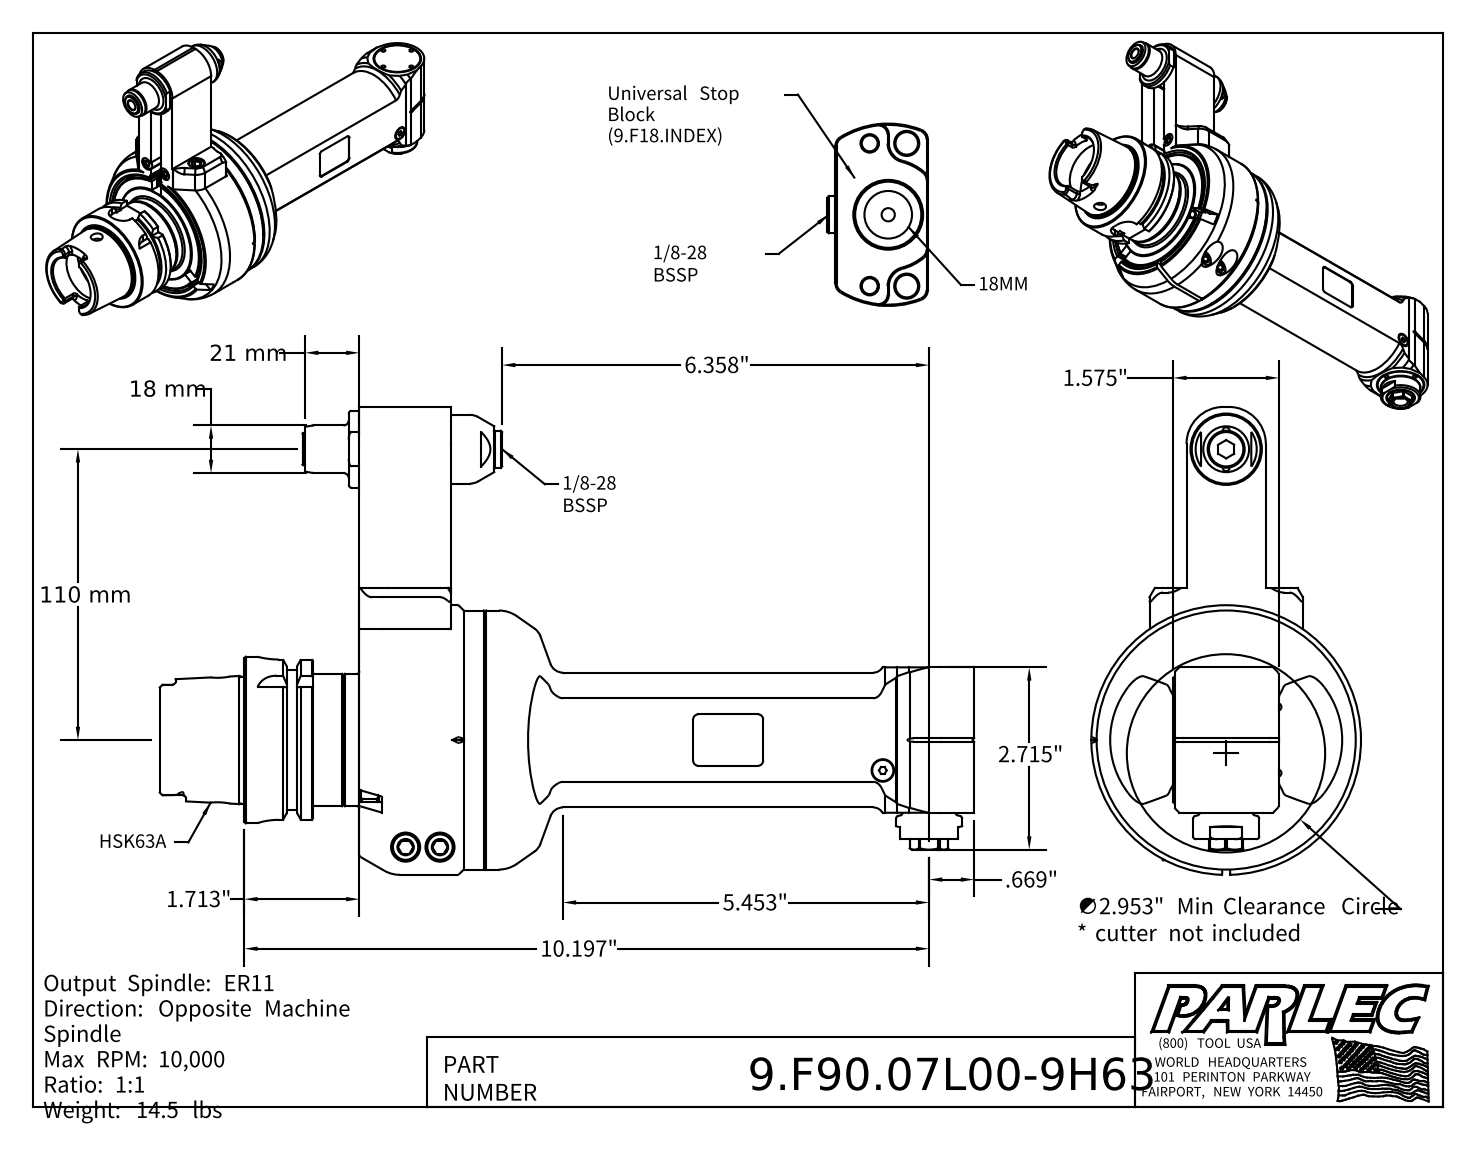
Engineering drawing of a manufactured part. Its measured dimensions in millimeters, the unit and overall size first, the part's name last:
Units: millimetres
Overall size (bounding box): 308 × 176.98 × 102
Round holes (diameter × count): ⌀2.6 ×6, ⌀4.2 ×4, ⌀6.5 ×3, ⌀3.3 ×2, ⌀7.5 ×2, ⌀8 ×2, ⌀10.4 ×2, ⌀11 ×2, ⌀12.5 ×2, ⌀2.5 ×1, ⌀3 ×1, ⌀5 ×1
Round bosses / shafts (diameter × count): ⌀10 ×4, ⌀18 ×3, ⌀12 ×2, ⌀8 ×2, ⌀6 ×2, ⌀2.5 ×2, ⌀102 ×1, ⌀98 ×1
Partial cylindrical surfaces — rounded edges, fillets, slot ends (radius × count): R1 ×14, R2 ×12, R1.5 ×6, R3 ×6, R8 ×6, R2.88 ×4, R4 ×4, R0.4 ×2
Main face-to-face distances: 5, 35, 26, 40, 24.5, 8.5, 15.5, 34.5, 7, 30
Hole centre spacings: 12.5, 17.68, 7, 25, 50.64, 53.6, 60.53, 67.48
Volume: 1 001 000 mm³ · Surface area: 125 848 mm²
Bodies: 1 solid, 640 faces (280 planar, 182 cylindrical, 178 other)
Part name (STEP PRODUCT): 9.F90.07L00-9H63
STEP written by: Autodesk Inventor 2022 (AUTOMOTIVE_DESIGN)
